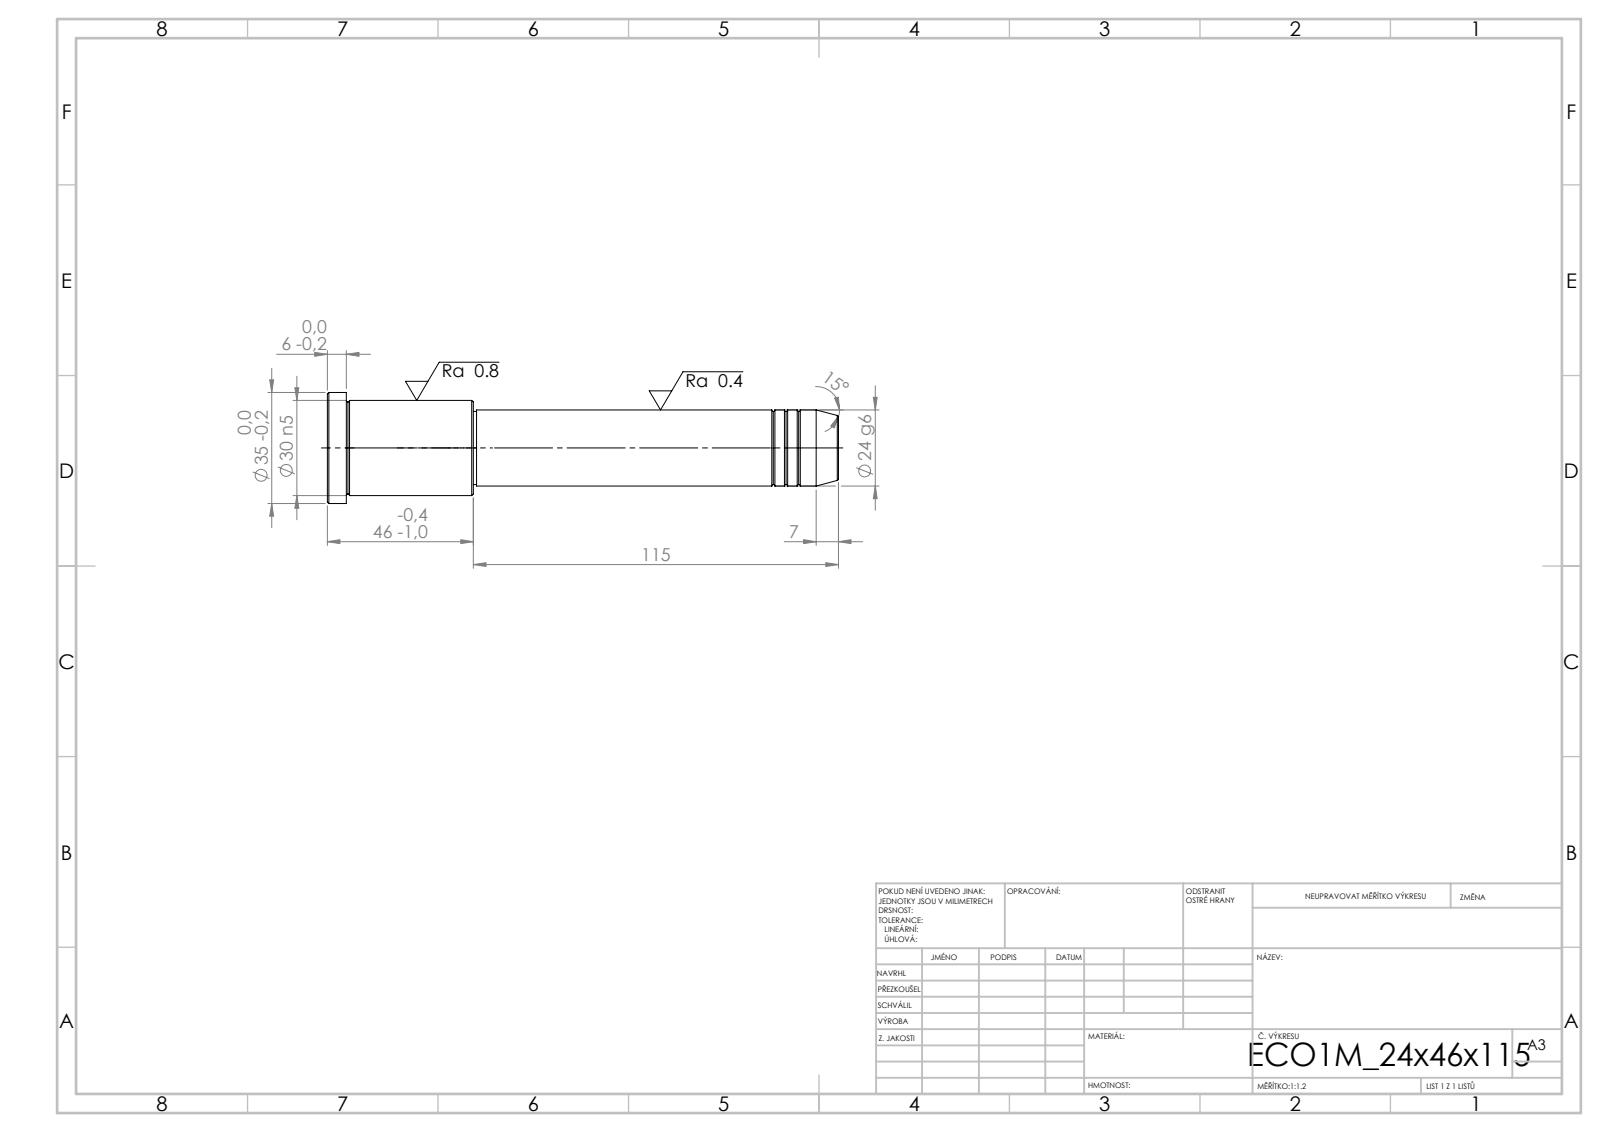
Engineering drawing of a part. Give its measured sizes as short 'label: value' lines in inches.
written by: SolidWorks 2019 (CONFIG_CONTROL_DESIGN)
unit: in
bodies: 1 solid, 43 faces (5 planar, 14 cylindrical, 24 other)
size: 6.339 × 1.378 × 1.378
volume: 5.212 in³; area: 23.32 in²
bosses: 1× ⌀1.378, 1× ⌀1.181, 1× ⌀0.945, 1× ⌀0.906
face distances: 6.339, 6.102, 0.236, 4.528, 1.575, 1.811, 4.488, 0.039, 1.614, 1.85
